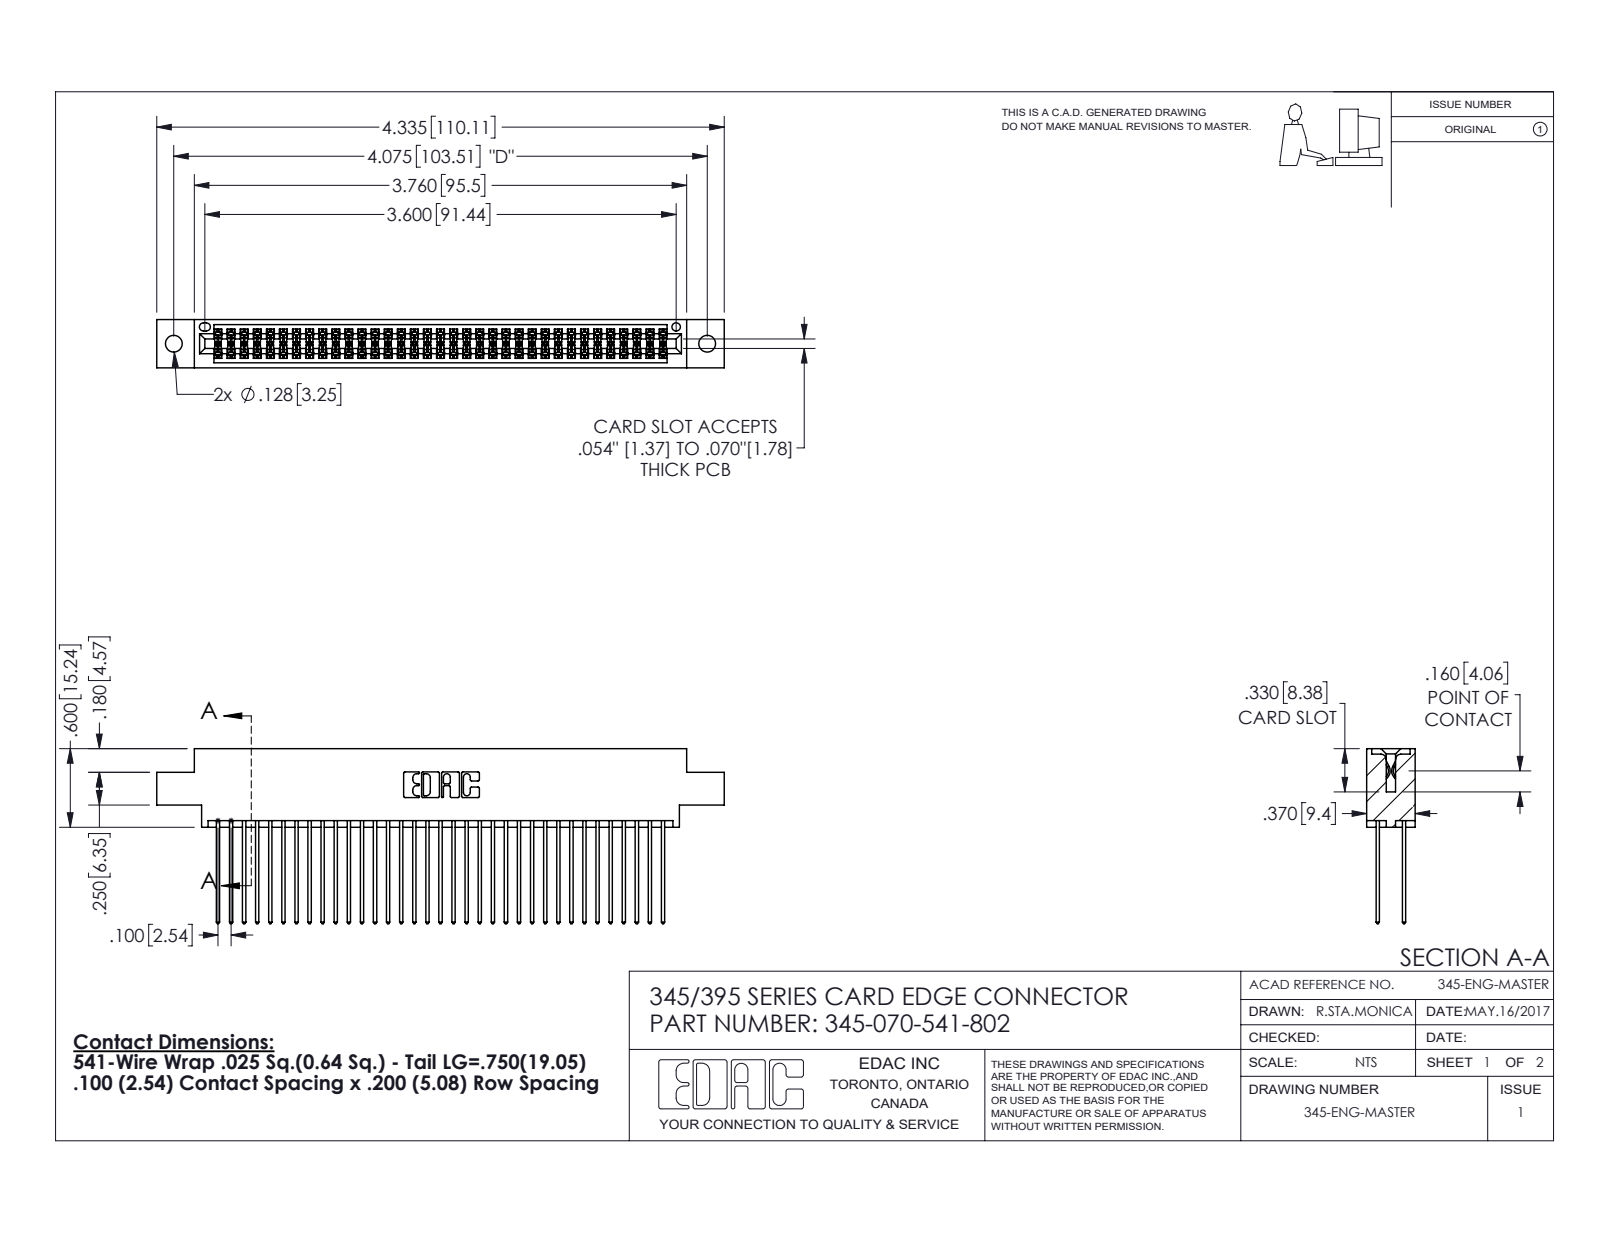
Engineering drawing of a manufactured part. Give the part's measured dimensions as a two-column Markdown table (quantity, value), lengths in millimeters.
| quantity | value |
| --- | --- |
| part name | 345-070-541-802; 345-292-001_345-293-141; 345 Part_0.170 Offset - 0.128 Dia |
| STEP written by | SolidWorks 2016 (CONFIG_CONTROL_DESIGN) |
| units | millimeters |
| bodies | 71 solids, 3630 faces (2394 planar, 1236 cylindrical, 0 other) |
| overall size | 110.1 × 34 × 9.4 |
| volume | 10 900 mm³ |
| surface area | 17 710 mm² |
| round holes (diameter × count) | 3.3 × 2, 1.6 × 1 |
| partial cylindrical surfaces (radius × count) | 0.2 × 105, 0.3 × 70, 0.3 × 22, 0.2 × 6, 0.8 × 6, 0.7 × 3, 0.4 × 2, 0.5 × 2 |
| main face-to-face distances | 7.6, 1.8, 5.1, 2.5, 6.9, 0.6, 9.4, 5.7, 4.4, 3.8 |
| hole center spacings | 6.9, 97.5, 103.5 |
